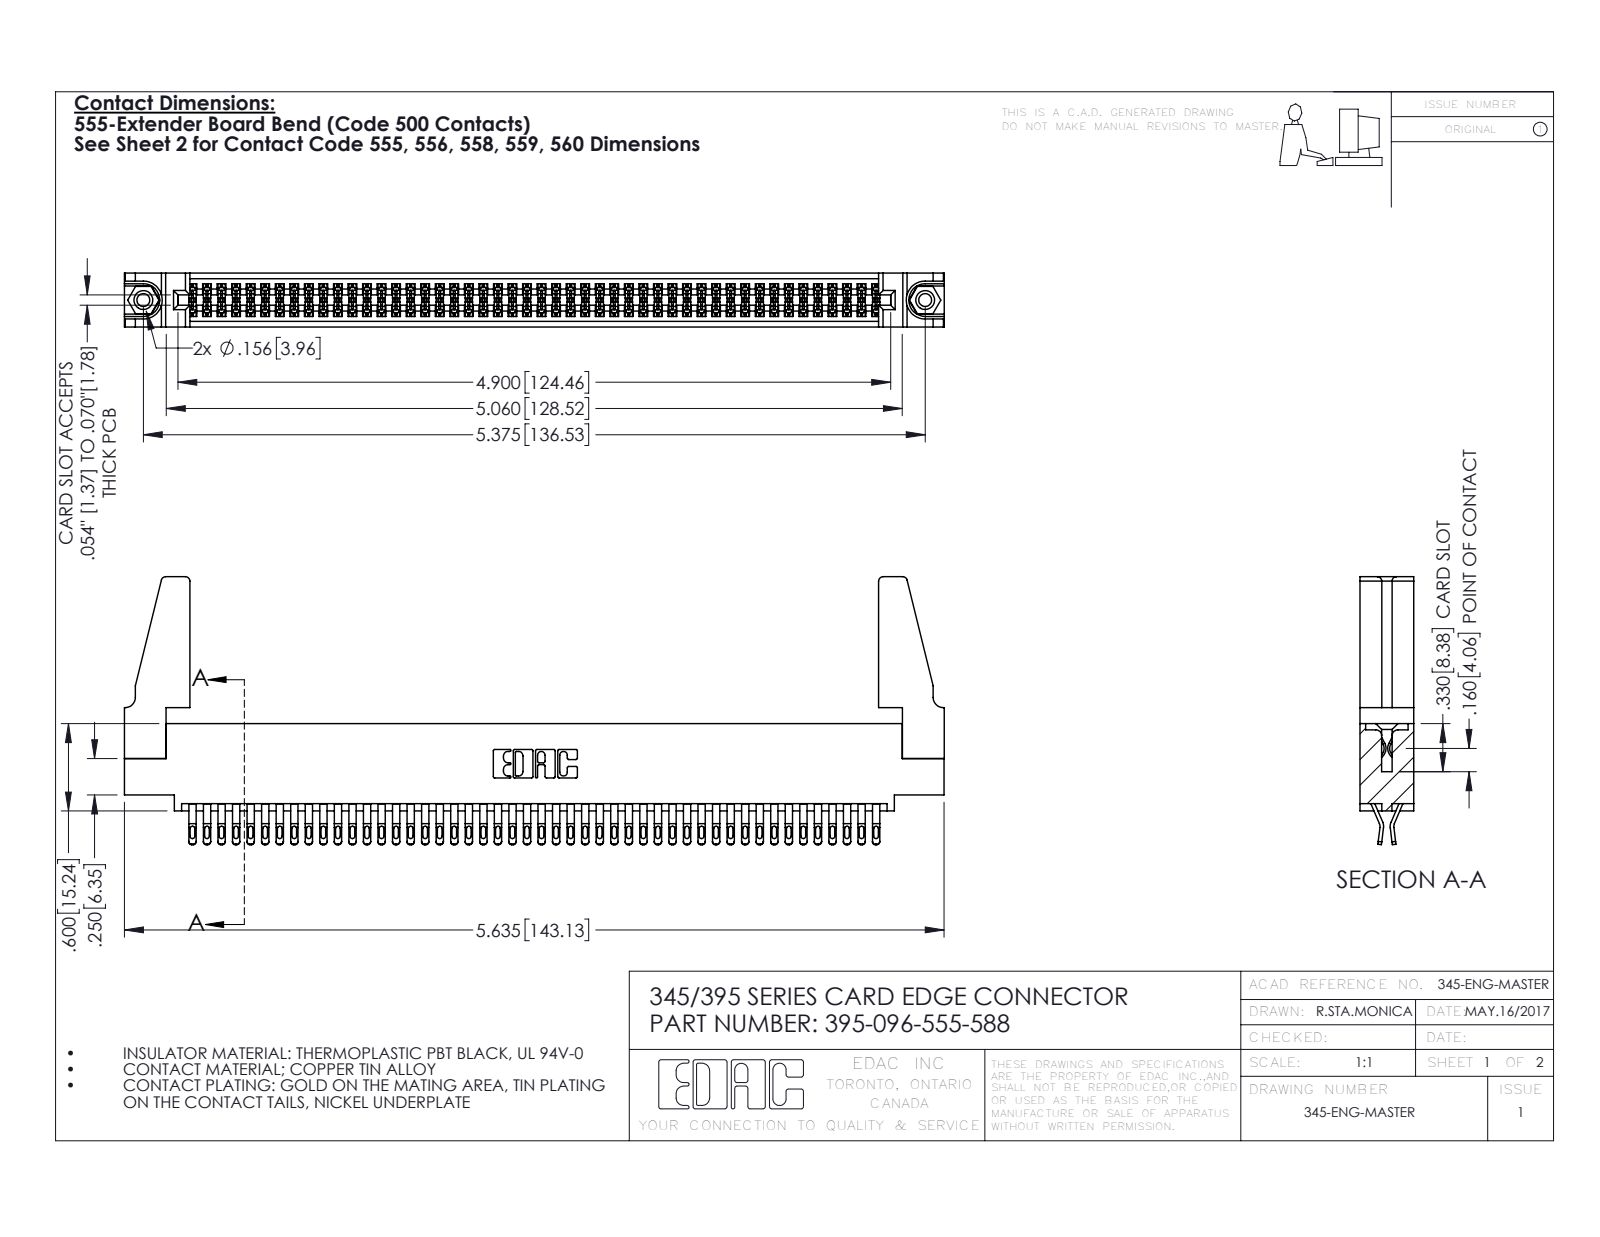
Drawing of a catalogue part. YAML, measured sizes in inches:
part_name: "345-220-078_345-220-088; 345-250-001_345-250-001-102; 345 Part_0.110 Offset - 0.156 Dia-TH; 345-292-001_555 Tail (+1 more)"
step_written_by: "SolidWorks 2016 (CONFIG_CONTROL_DESIGN)"
units: inches
bodies: {solids: 101, faces: 5630, planar: 3132, cylindrical: 2482, other: 16}
overall_size: [5.636, 1.842, 0.37]
volume: 1.063
surface_area: 39.12
round_holes:
  - {diameter: 0.089, count: 2}
  - {diameter: 0.125, count: 2}
  - {diameter: 0.156, count: 2}
  - {diameter: 0.064, count: 1}
round_bosses_or_shafts:
  - {diameter: 0.155, count: 2}
partial_cylinders:
  - {radius: 0.016, count: 240}
  - {radius: 0.02, count: 192}
  - {radius: 0.006, count: 144}
  - {radius: 0.01, count: 22}
  - {radius: 0.03, count: 8}
  - {radius: 0.007, count: 6}
  - {radius: 0.031, count: 6}
  - {radius: 0.026, count: 3}
face_to_face_distances: [0.072, 0.298, 0.37, 0.025, 0.2, 0.098, 0.272, 0.225, 0.175, 0.149]
hole_center_spacings: [0.27, 5.139, 5.375]
